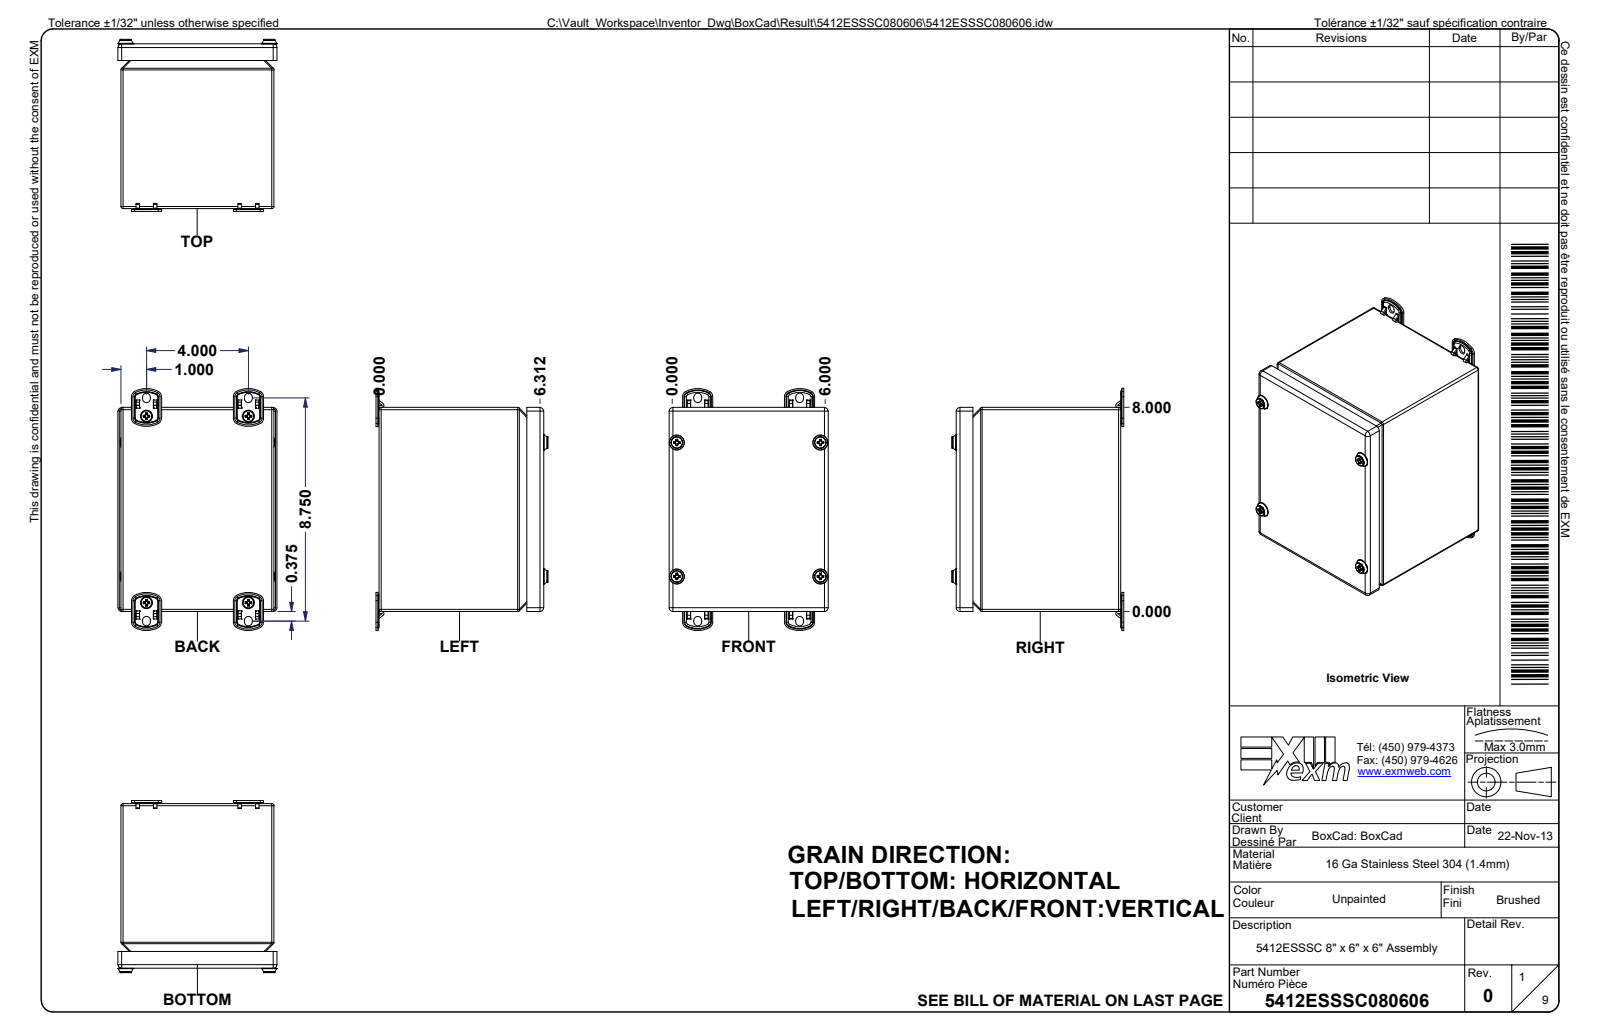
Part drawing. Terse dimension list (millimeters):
name: 5412ESSSC080606; 5412ESSSC080606B; 5412ESSSC080606B-P; STK-Q-08500 (+8 more)
written by: Autodesk Inventor 2024 (AUTOMOTIVE_DESIGN)
unit: mm
bodies: 39 solids, 4768 faces (2344 planar, 1164 cylindrical, 1260 other)
size: 241.2 × 171.4 × 158.4
volume: 333 800 mm³; area: 478 000 mm²
holes: 6× ⌀0.8, 6× ⌀5.1, 6× ⌀6.1, 4× ⌀4, 4× ⌀5, 4× ⌀5, 4× ⌀7, 4× ⌀7.9, 4× ⌀8.1
bosses: 8× ⌀5.9, 6× ⌀10, 6× ⌀0.9, 4× ⌀15, 4× ⌀13, 4× ⌀12.7, 4× ⌀7, 4× ⌀4.9
rounds: 252× R0.2, 82× R0.1, 56× R0.3, 48× R0.3, 28× R0.8, 28× R1, 24× R2.1, 24× R6
face distances: 1.3, 162.7, 151.1, 201.9, 164, 161.3, 152.4, 149.7, 203.2, 200.5
hole spacings: 126.1, 125.1, 192.6, 13.8, 21.7, 105.6, 143.1, 147.1
